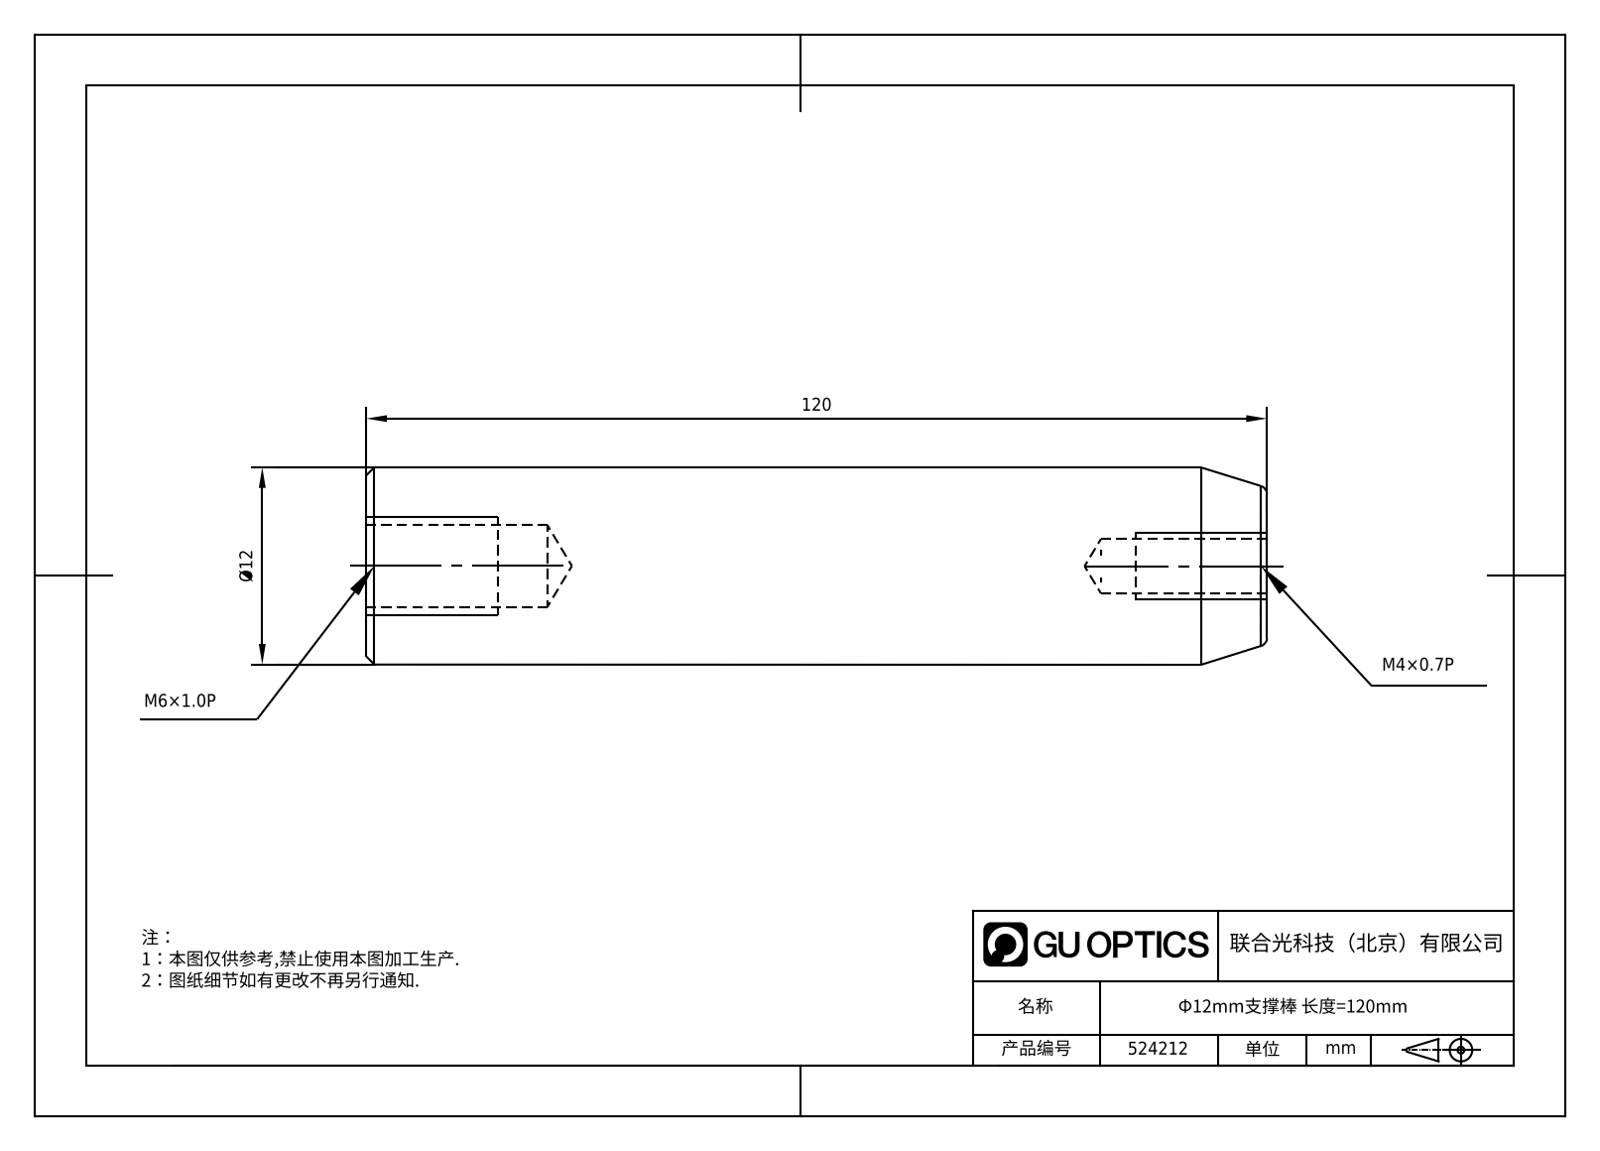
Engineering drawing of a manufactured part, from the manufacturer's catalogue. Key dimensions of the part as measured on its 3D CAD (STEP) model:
Part name (STEP PRODUCT): 524212
STEP written by: SolidWorks 2020 (CONFIG_CONTROL_DESIGN)
Units: millimetres
Bodies: 1 solid, 10 faces (2 planar, 3 cylindrical, 5 other)
Overall size (bounding box): 120 × 12 × 12
Volume: 13 164 mm³ · Surface area: 4 966 mm²
Round holes (diameter × count): ⌀3.3 ×1, ⌀5 ×1
Round bosses / shafts (diameter × count): ⌀12 ×1
Main face-to-face distances: 120
